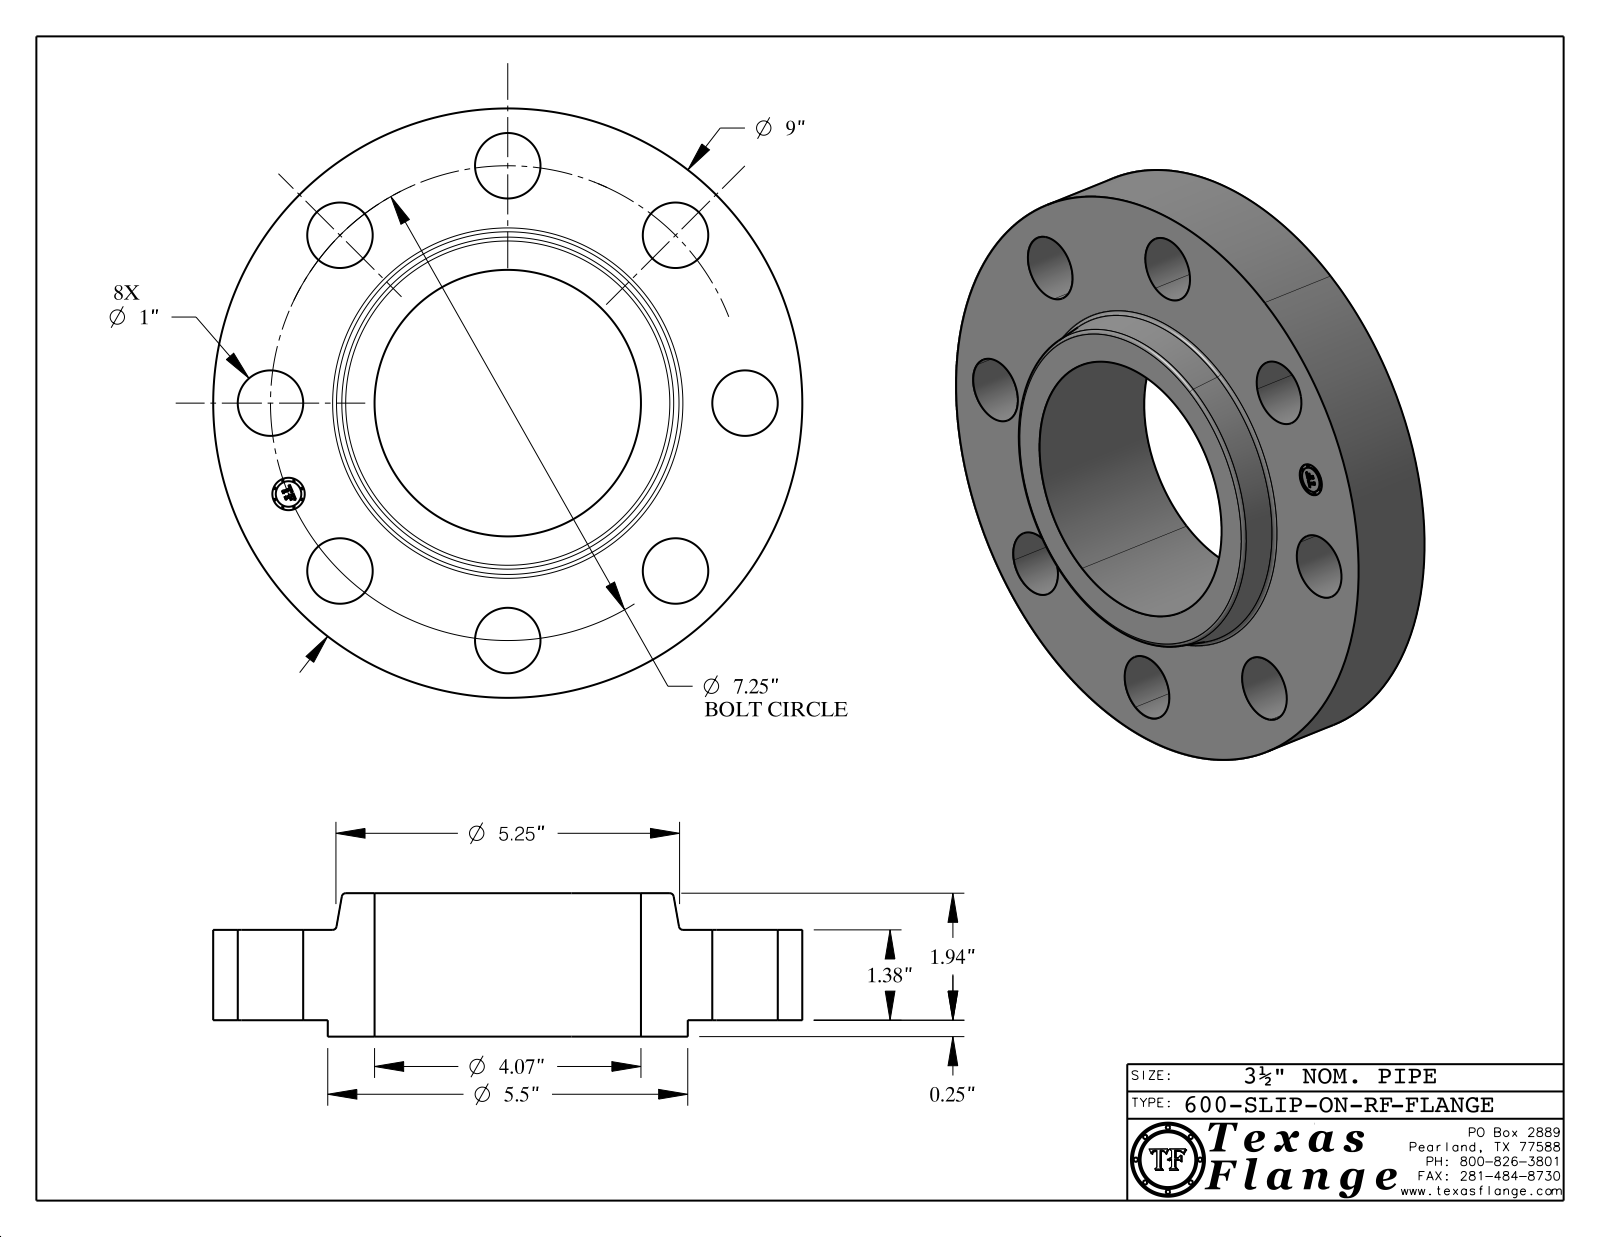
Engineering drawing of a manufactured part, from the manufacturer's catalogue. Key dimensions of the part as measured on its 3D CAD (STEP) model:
Part name (STEP PRODUCT): 600-SLIP-ON-RF
STEP written by: CATIA V5 STEP AP214 (AUTOMOTIVE_DESIGN)
Units: inches
Bodies: 1 solid, 417 faces (369 planar, 42 cylindrical, 6 other)
Overall size (bounding box): 9 × 9 × 2.19
Volume: 68.24 in³ · Surface area: 201.8 in²
Round holes (diameter × count): ⌀1 ×8, ⌀0.495 ×1, ⌀4.07 ×1
Round bosses / shafts (diameter × count): ⌀0.03 ×8, ⌀9 ×1, ⌀5.5 ×1, ⌀0.39 ×1
Main face-to-face distances: 1.38, 0.25, 1.63, 2.19, 1.94, 0.56, 1.615, 1.365, 0.015, 0.575
Hole centre spacings: 3.625, 2.774, 5.127, 6.698, 7.25, 1.415, 7.111, 4.028
